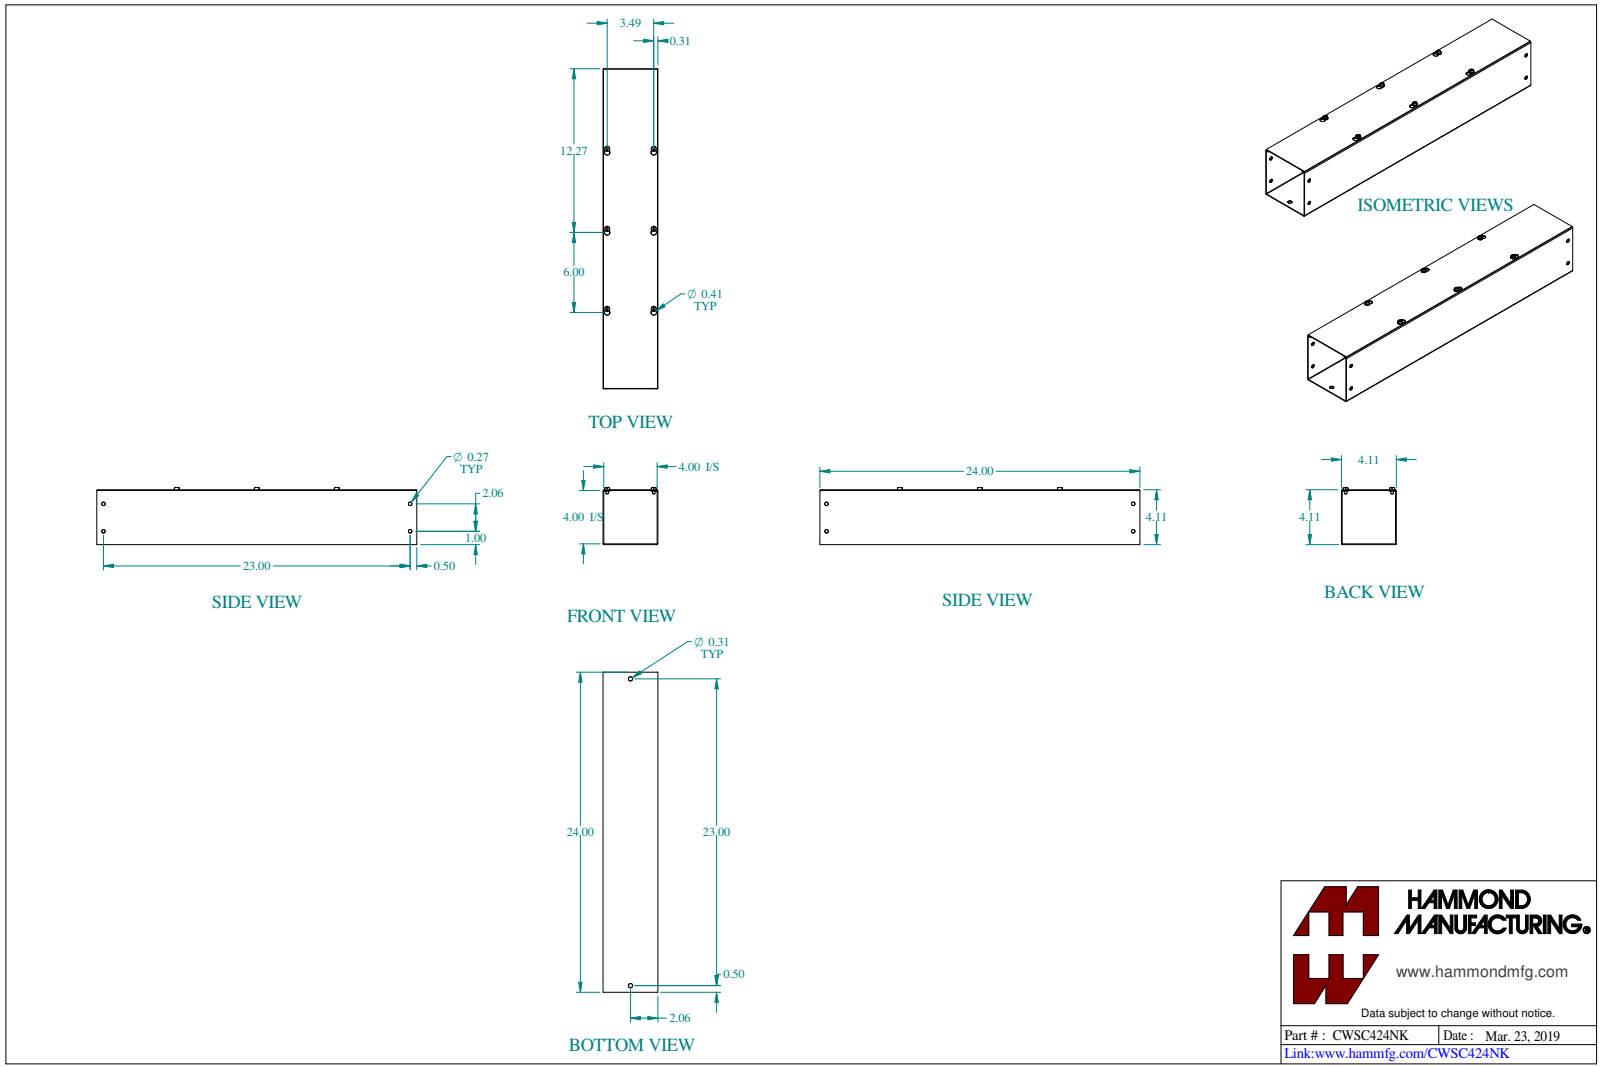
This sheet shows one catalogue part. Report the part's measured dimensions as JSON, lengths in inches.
{"part_name": "CWSC424NK", "step_written_by": "SolidWorks 2023 (CONFIG_CONTROL_DESIGN)", "units": "inches", "bodies": {"solids": 8, "faces": 242, "planar": 118, "cylindrical": 88, "other": 36}, "overall_size": [24, 4.289, 4.114], "volume_in3": 23.16, "surface_area_in2": 819.8, "round_holes": [[0.177, 6], [0.266, 4], [0.313, 2]], "round_bosses_or_shafts": [[0.375, 6], [0.19, 6]], "partial_cylinders_radius": [[0.125, 6], [0.203, 6], [0.029, 4], [0.086, 4]], "face_to_face_distances": [0.057, 4.057, 4, 4.114, 3.943, 0.114, 0.031, 4.083, 0.026, 4.026], "hole_center_spacings": [5.77, 6, 6.941, 11.631, 17.587, 3.489, 23, 2.057]}
